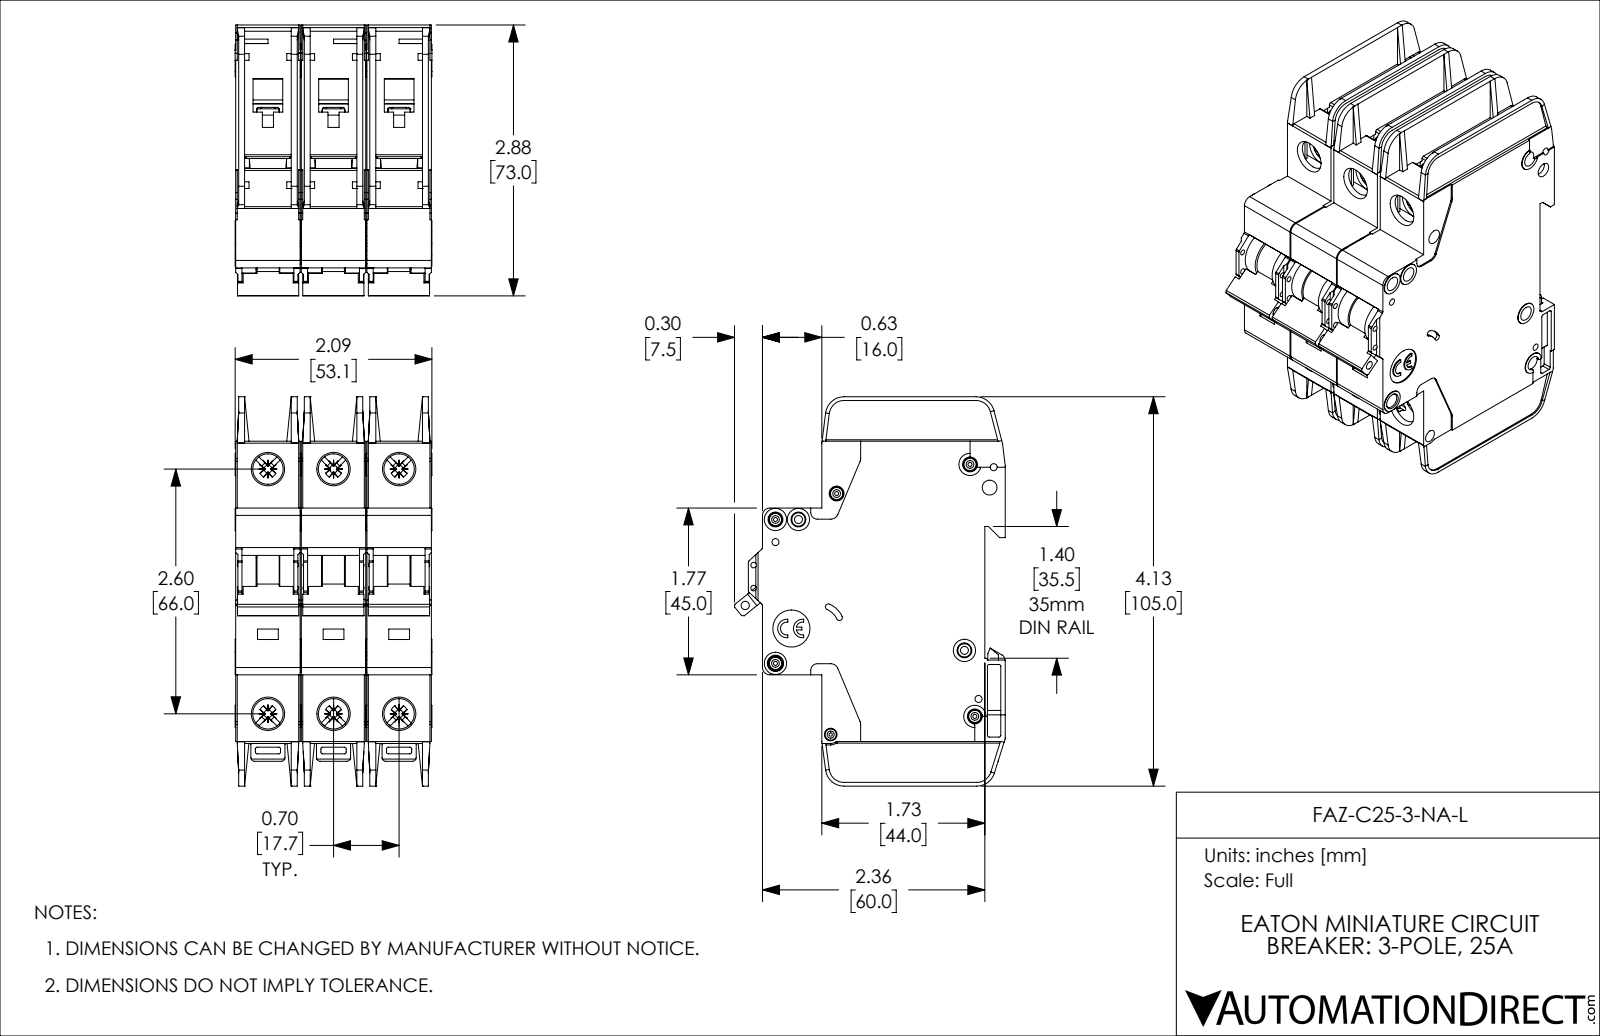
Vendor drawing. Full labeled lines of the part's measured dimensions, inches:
Part name (STEP PRODUCT): FAZ-C25-3-NA-L
STEP written by: SolidWorks 2019 (AUTOMOTIVE_DESIGN)
Units: inches
Bodies: 3 solids, 3381 faces (2013 planar, 1071 cylindrical, 297 other)
Overall size (bounding box): 4.134 × 2.876 × 2.091
Volume: 14.05 in³ · Surface area: 123 in²
Round holes (diameter × count): ⌀0.157 ×8, ⌀0.323 ×6, ⌀0.043 ×5, ⌀0.075 ×4, ⌀0.059 ×2, ⌀0.085 ×2, ⌀0.035 ×1, ⌀0.089 ×1, ⌀0.098 ×1, ⌀0.134 ×1, ⌀0.394 ×1
Round bosses / shafts (diameter × count): ⌀0.13 ×5, ⌀0.236 ×4, ⌀0.118 ×4, ⌀0.098 ×3
Partial cylindrical surfaces — rounded edges, fillets, slot ends (radius × count): R0.02 ×72, R0.016 ×30, R0.039 ×18, R0.043 ×12, R0.079 ×12, R0.008 ×6, R0.01 ×6, R0.028 ×6
Main face-to-face distances: 0.697, 0.047, 1.394, 0.685, 0.591, 1.382, 0.744, 0.65, 0.106, 0.094
Hole centre spacings: 0.697, 2.69, 2.598, 0.244, 0.537, 0.87, 1.394, 2.948
